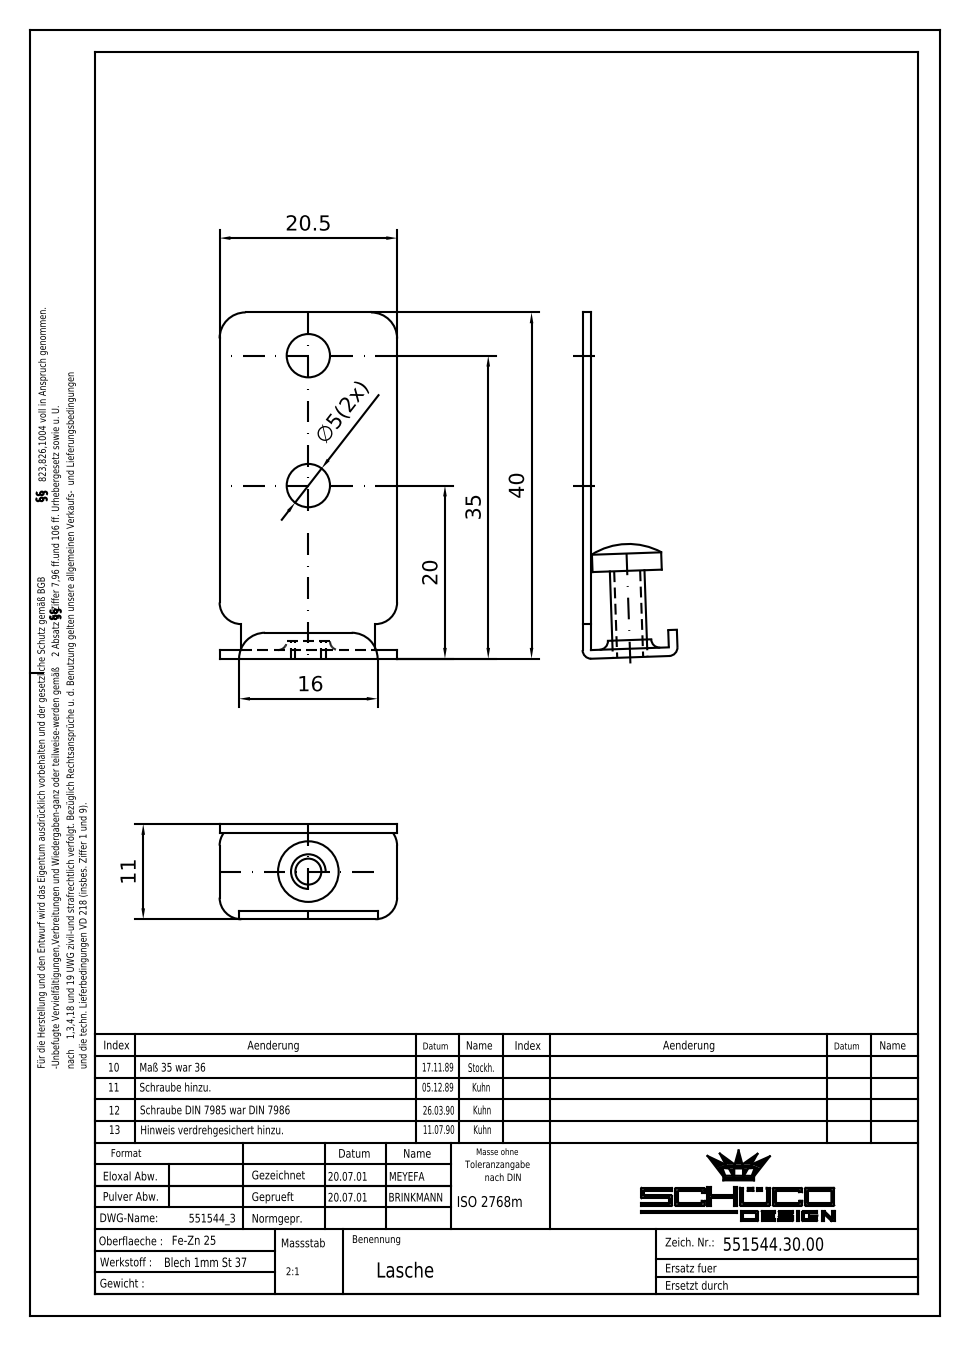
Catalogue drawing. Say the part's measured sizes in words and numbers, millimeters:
The part is named "KD-114927". Its 3-D file was written by "Autodesk Inventor 2024 (AUTOMOTIVE_DESIGN)". It is 1 solid with 42 faces: 26 planar, 16 cylindrical and 0 other. Overall it measures 38.93 by 20.5 by 10.93 millimeters. Its volume is 960 cubic millimeters and its surface area 2 074 square millimeters. Round holes: 2 of diameter 5, 1 of diameter 3.24. Round bosses or shafts: 1 of diameter 7. Partial cylindrical surfaces (rounded edges, fillets, slot ends): 6 of radius 2, 2 of radius 1, 2 of radius 2.5, 2 of radius 3. The main face-to-face distances are 1, 2, 20.5, 3, 2.25, 18.25, 16, 6.92, 7.92, 8.92. The hole center spacings are 15.
